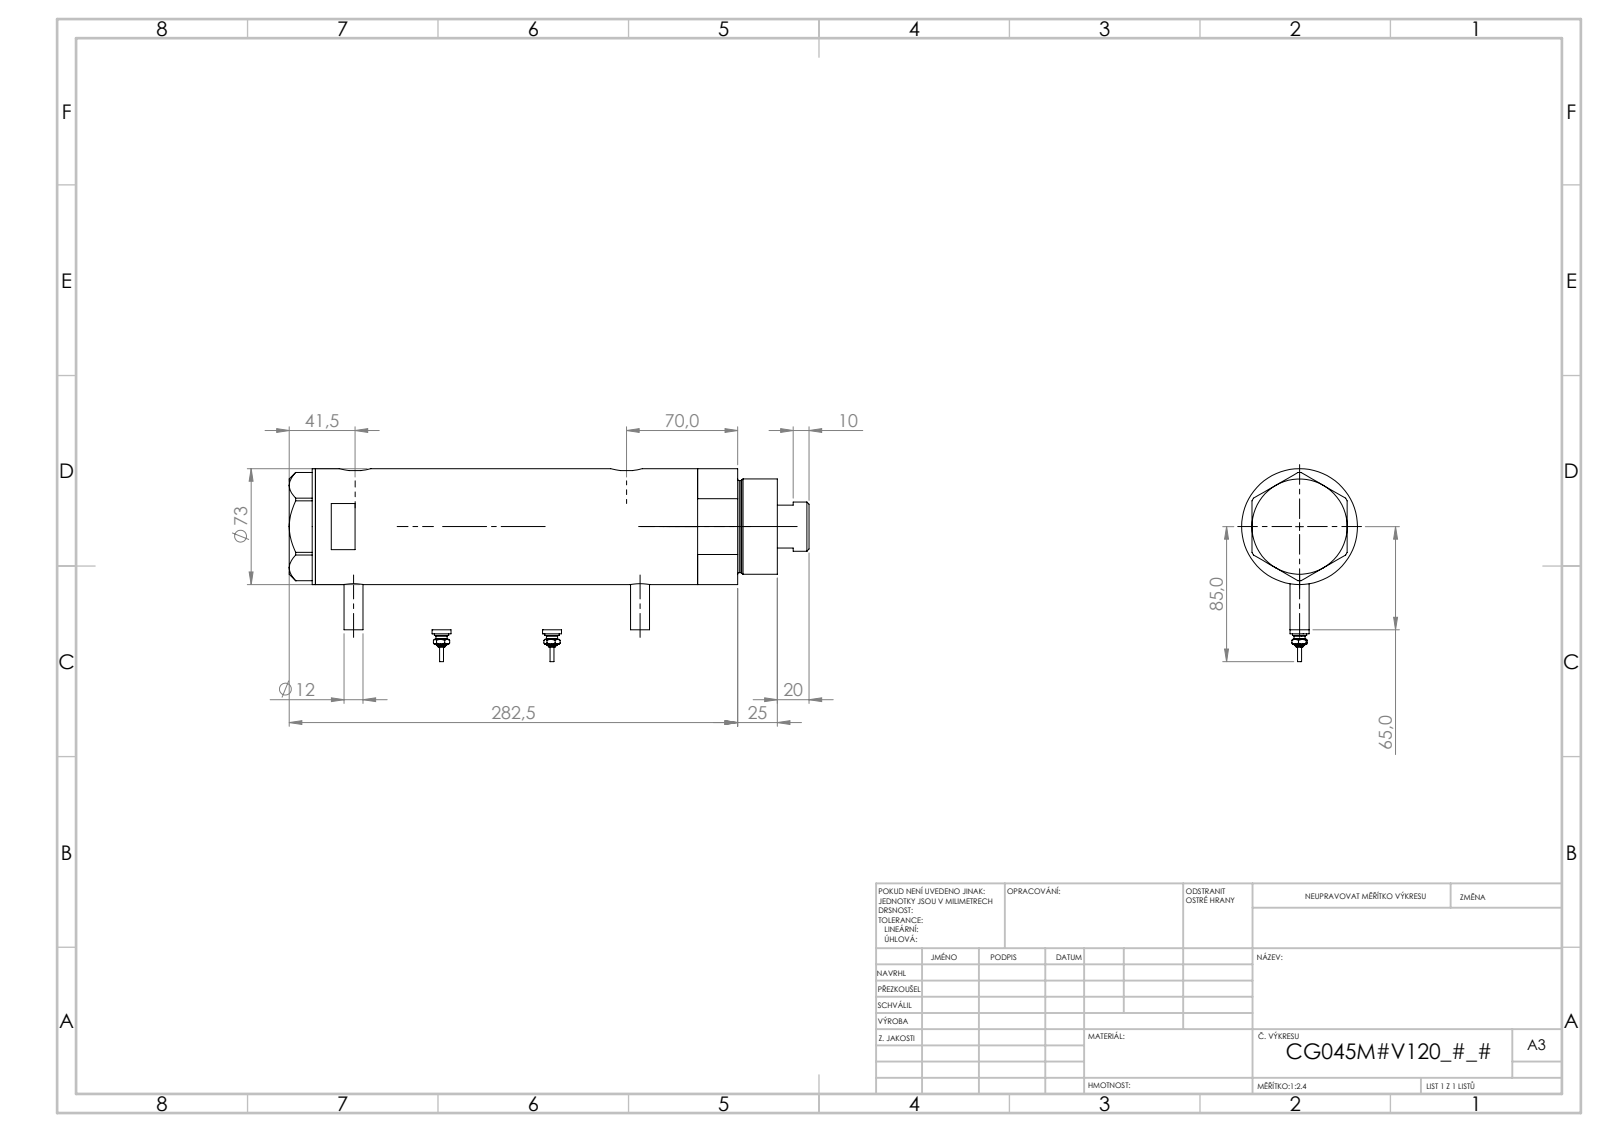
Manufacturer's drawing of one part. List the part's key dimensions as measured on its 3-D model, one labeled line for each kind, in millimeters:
Part name (STEP PRODUCT): V270CG_BACK; V270CG_MIDDLE; V270CG_VC; V270CG_FRONT (+1 more)
STEP written by: SolidWorks 2019 (CONFIG_CONTROL_DESIGN)
Units: millimetres
Bodies: 6 solids, 231 faces (78 planar, 79 cylindrical, 74 other)
Overall size (bounding box): 311.52 × 105.3 × 73
Volume: 1 078 000 mm³ · Surface area: 178 436 mm²
Round holes (diameter × count): ⌀5 ×2, ⌀12.5 ×2, ⌀13.16 ×2, ⌀10.5 ×1, ⌀32 ×1, ⌀33.5 ×1, ⌀45 ×1, ⌀48 ×1, ⌀64 ×1
Round bosses / shafts (diameter × count): ⌀12 ×3, ⌀9 ×2, ⌀7 ×2, ⌀4.34 ×2, ⌀2.4 ×2, ⌀73 ×1, ⌀60 ×1, ⌀58 ×1
Partial cylindrical surfaces — rounded edges, fillets, slot ends (radius × count): R10 ×2
Main face-to-face distances: 187.14, 26, 161.14, 16.5, 42.5, 203.64, 275.01, 291.51, 249.01, 87.87
Hole centre spacings: 171.65, 0.99, 1, 8.5, 8.51, 162.15, 163.14, 163.15
